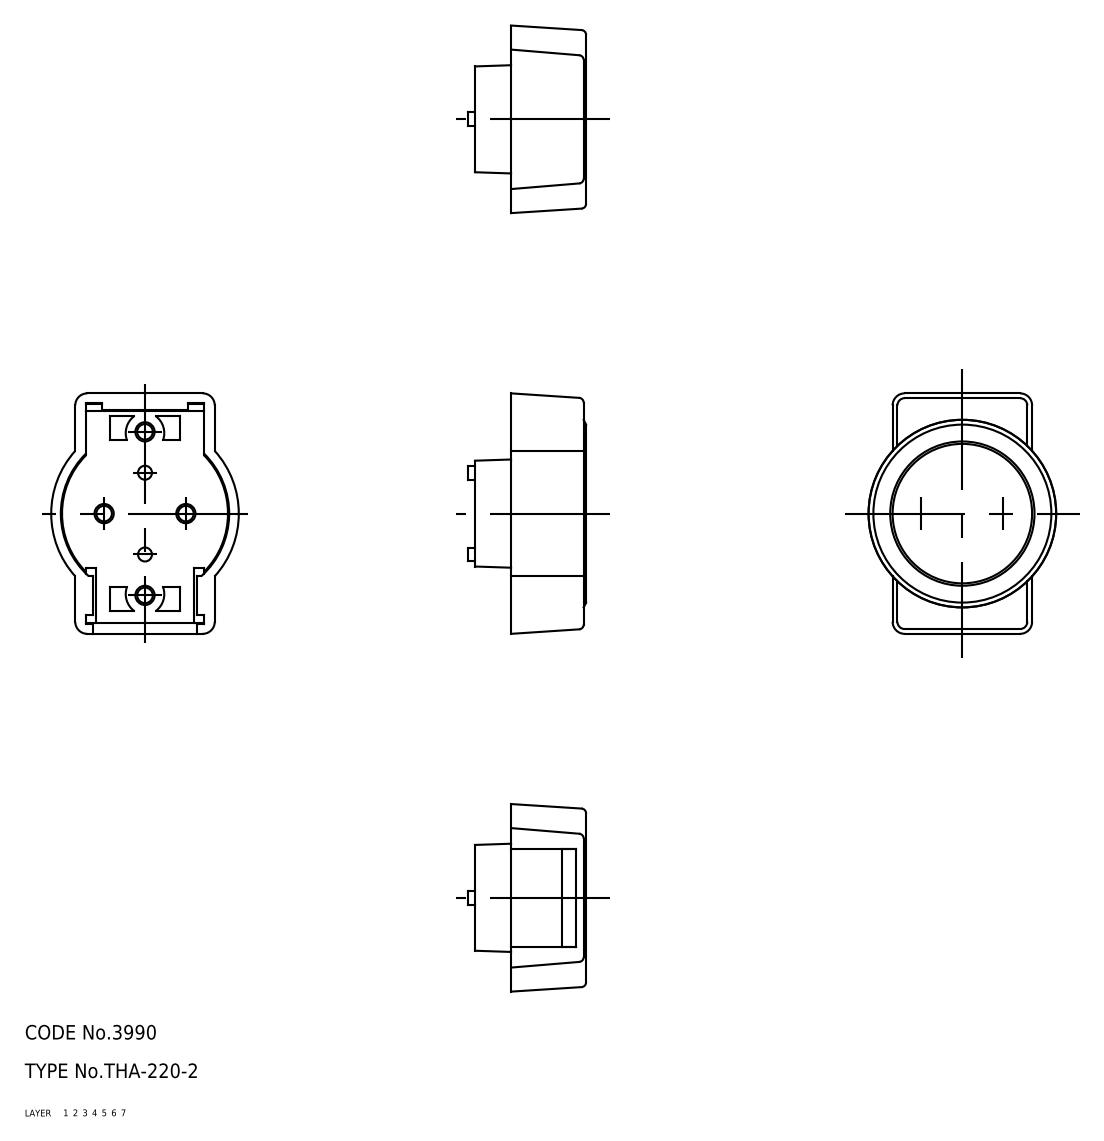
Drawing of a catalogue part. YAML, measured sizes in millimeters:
part_name: "cover; base_B; base_A; THA_220_2_24155_36"
step_written_by: "CADfix (AUTOMOTIVE_DESIGN)"
units: millimeters
bodies: {solids: 3, faces: 142, planar: 0, cylindrical: 0, other: 142}
overall_size: [50, 39, 24.6]
volume: 17508
surface_area: 14244
